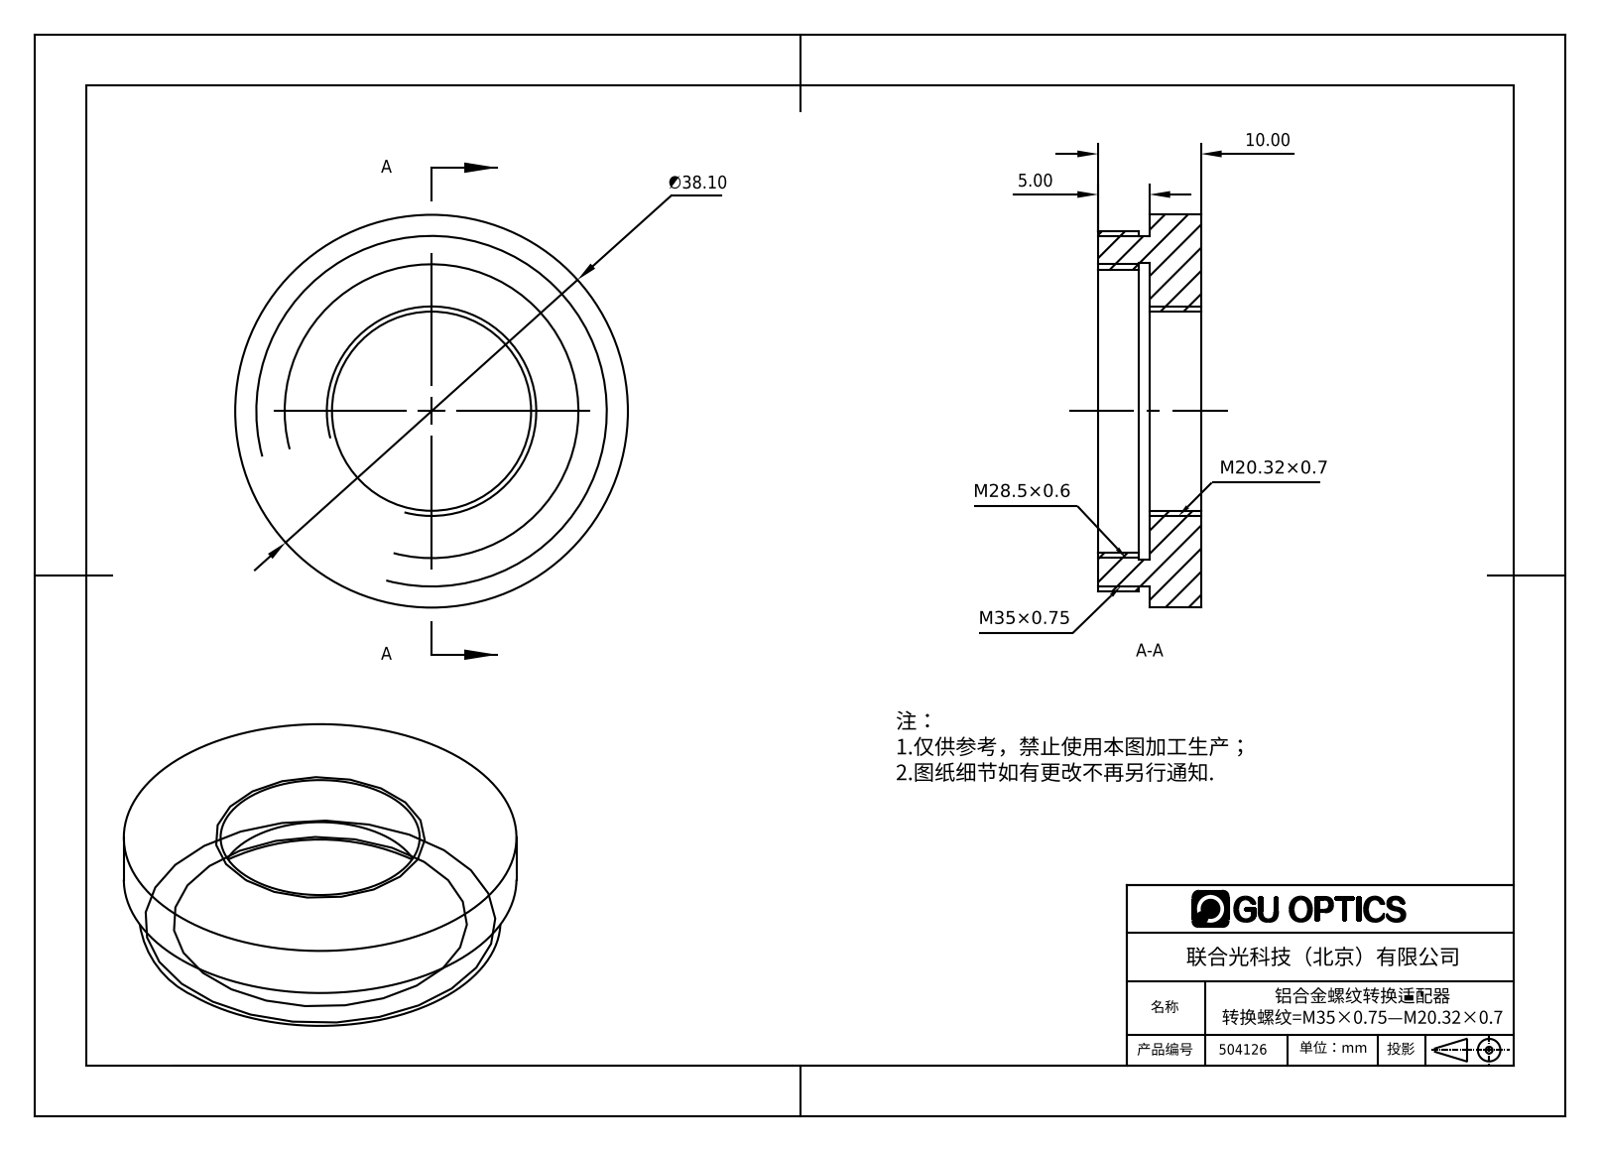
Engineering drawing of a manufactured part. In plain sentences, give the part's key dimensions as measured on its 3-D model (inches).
The part is named "504126". Its 3-D file was written by "SolidWorks 2016 (AUTOMOTIVE_DESIGN)". It is 1 solid with 18 faces: 6 planar, 12 cylindrical and 0 other. Overall it measures 1.5 by 1.5 by 0.394 inches. Its volume is 0.364 cubic inches and its surface area 5.879 square inches. Round holes: 1 of diameter 0.761, 1 of diameter 1.083, 1 of diameter 1.13. Round bosses or shafts: 1 of diameter 1.5, 1 of diameter 1.378, 1 of diameter 1.339. The main face-to-face distances are 0.197, 0.394, 0.157, 0.039, 0.236.
